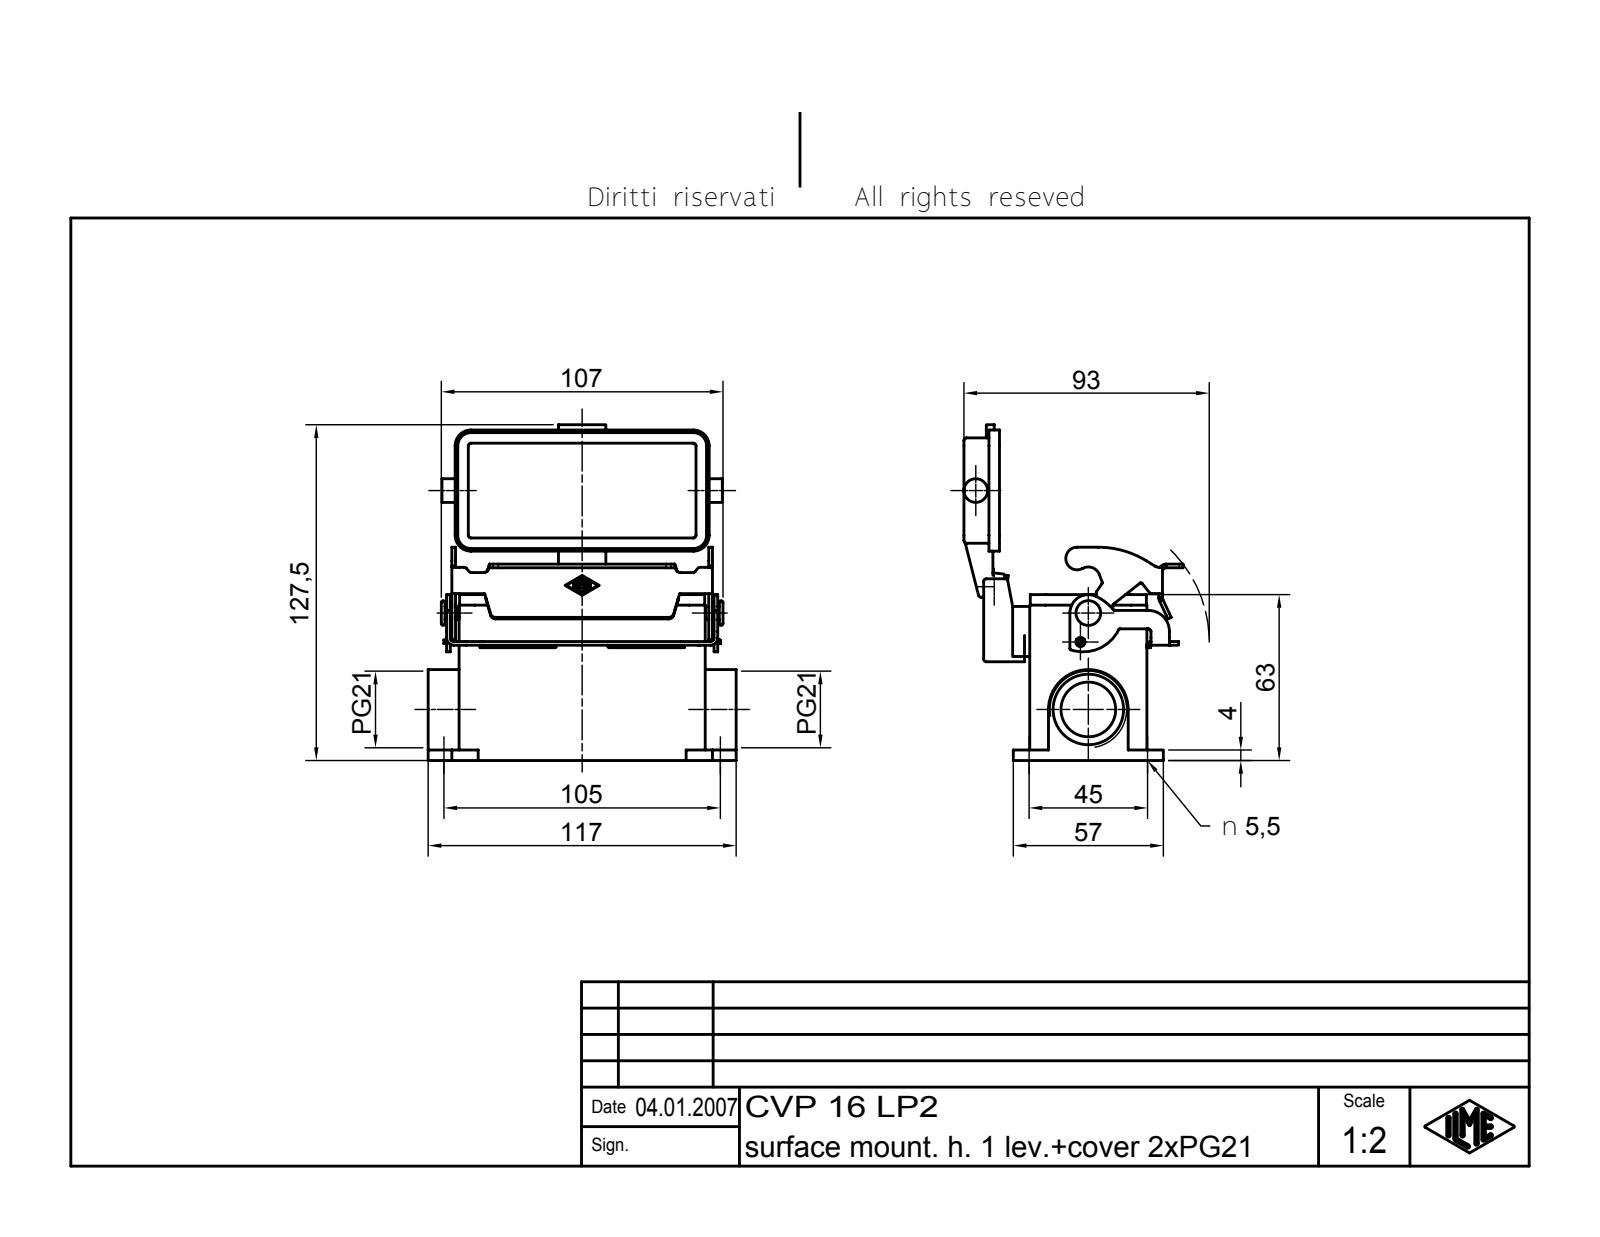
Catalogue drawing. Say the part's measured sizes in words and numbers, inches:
The part is named "CVP 16 LP2". Its 3-D file was written by "Autodesk Inventor 7 (AUTOMOTIVE_DESIGN)". It is 4 solids with 590 faces: 232 planar, 193 cylindrical and 165 other. Overall it measures 5.02 by 4.606 by 3.277 inches. Its volume is 7.995 cubic inches and its surface area 123.4 square inches. Round holes: 4 of diameter 0.217, 1 of diameter 0.138, 1 of diameter 0.157, 1 of diameter 0.818, 1 of diameter 1.054. Round bosses or shafts: 2 of diameter 0.197, 1 of diameter 0.354, 1 of diameter 0.276, 1 of diameter 0.126, 1 of diameter 0.118. Partial cylindrical surfaces (rounded edges, fillets, slot ends): 32 of radius 0.039, 15 of radius 0.01, 10 of radius 0.02, 9 of radius 0.059, 8 of radius 0.236, 7 of radius 0.079, 6 of radius 0.055, 6 of radius 0.11. The main face-to-face distances are 0.157, 1.594, 1.752, 1.437, 0.079, 2.736, 2.579, 1.142, 0.984, 0.059. The hole center spacings are 1.772, 4.134, 4.498, 1.015.
